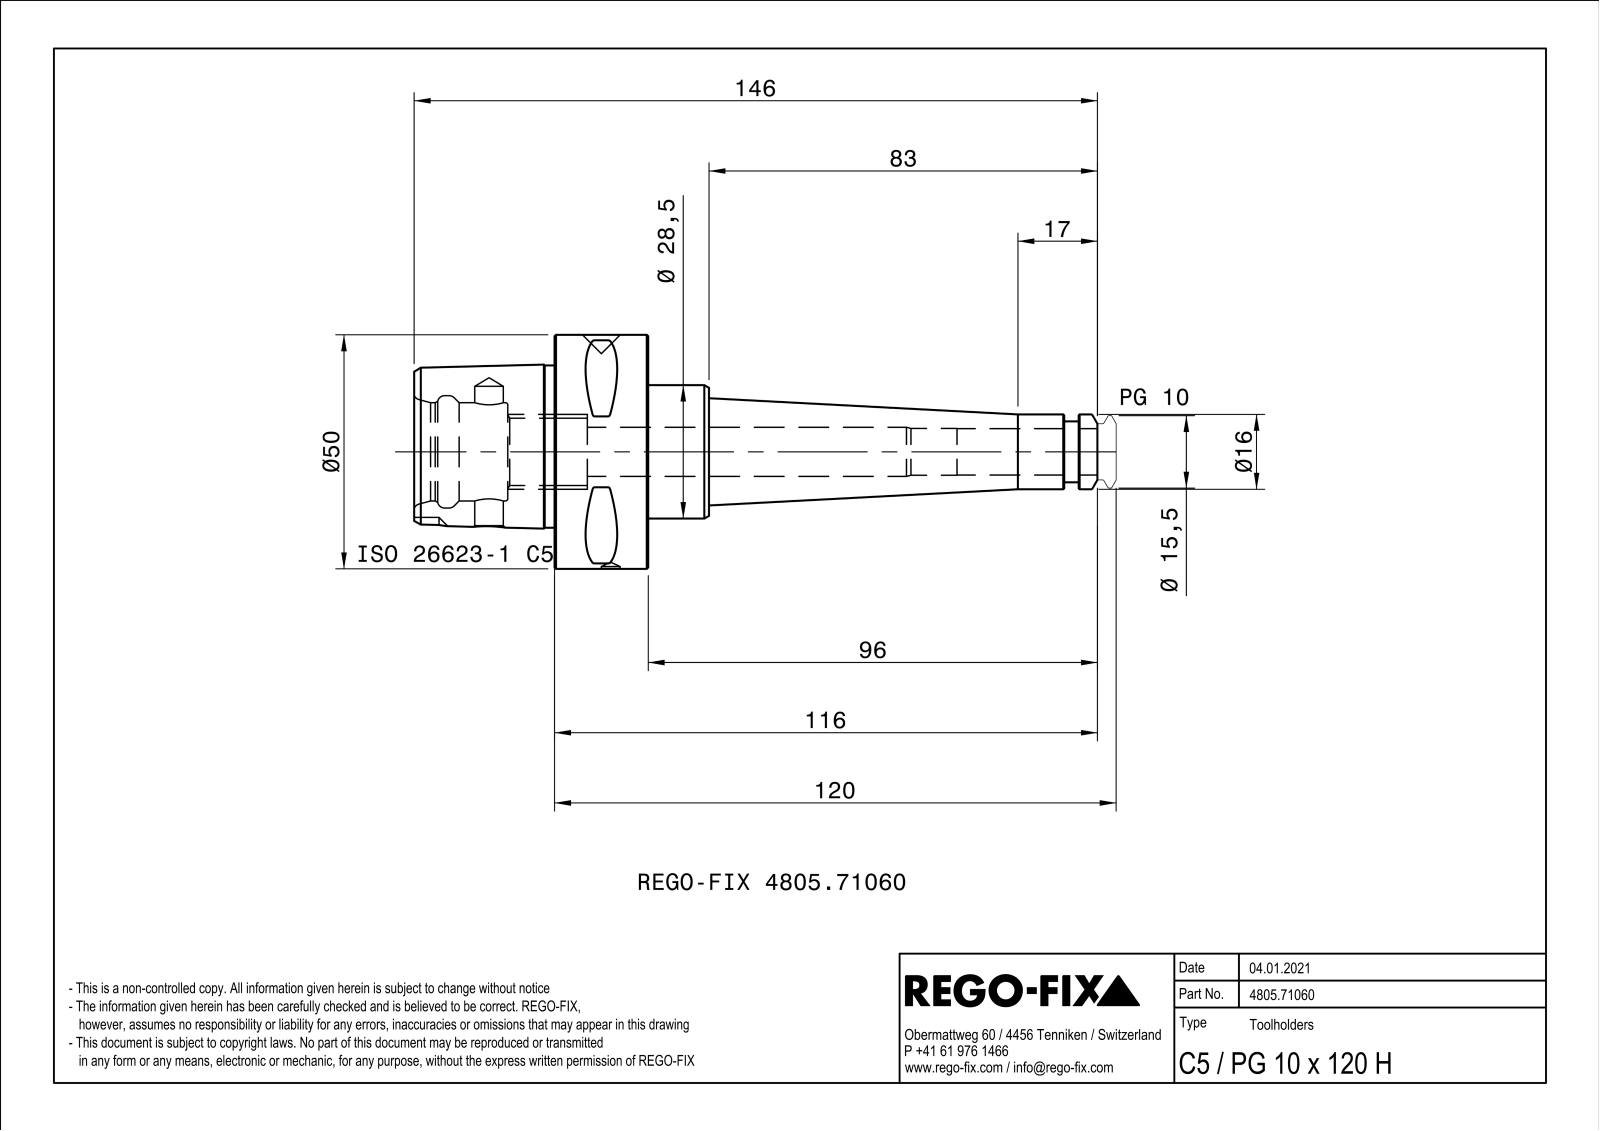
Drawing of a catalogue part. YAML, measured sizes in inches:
part_name: "NOCUT"
step_written_by: "SIEMENS PLM Software Solid Edge ST10 (AUTOMOTIVE_DESIGN)"
units: inches
bodies: {solids: 1, faces: 120, planar: 24, cylindrical: 26, other: 70}
overall_size: [5.748, 1.969, 1.969]
volume: 4.68
surface_area: 33.94
round_holes:
  - {diameter: 0.157, count: 1}
  - {diameter: 0.24, count: 1}
  - {diameter: 0.394, count: 1}
  - {diameter: 0.413, count: 1}
  - {diameter: 0.566, count: 1}
  - {diameter: 0.827, count: 1}
  - {diameter: 0.945, count: 1}
round_bosses_or_shafts:
  - {diameter: 1.969, count: 1}
  - {diameter: 1.122, count: 1}
  - {diameter: 0.63, count: 1}
  - {diameter: 0.512, count: 1}
partial_cylinders:
  - {radius: 0.02, count: 8}
  - {radius: 0.157, count: 1}
face_to_face_distances: [0.787, 1.181, 1.969, 0.755, 1.748, 0.512, 1.299, 2.48, 1.693, 0.394]
hole_center_spacings: [1.024]
